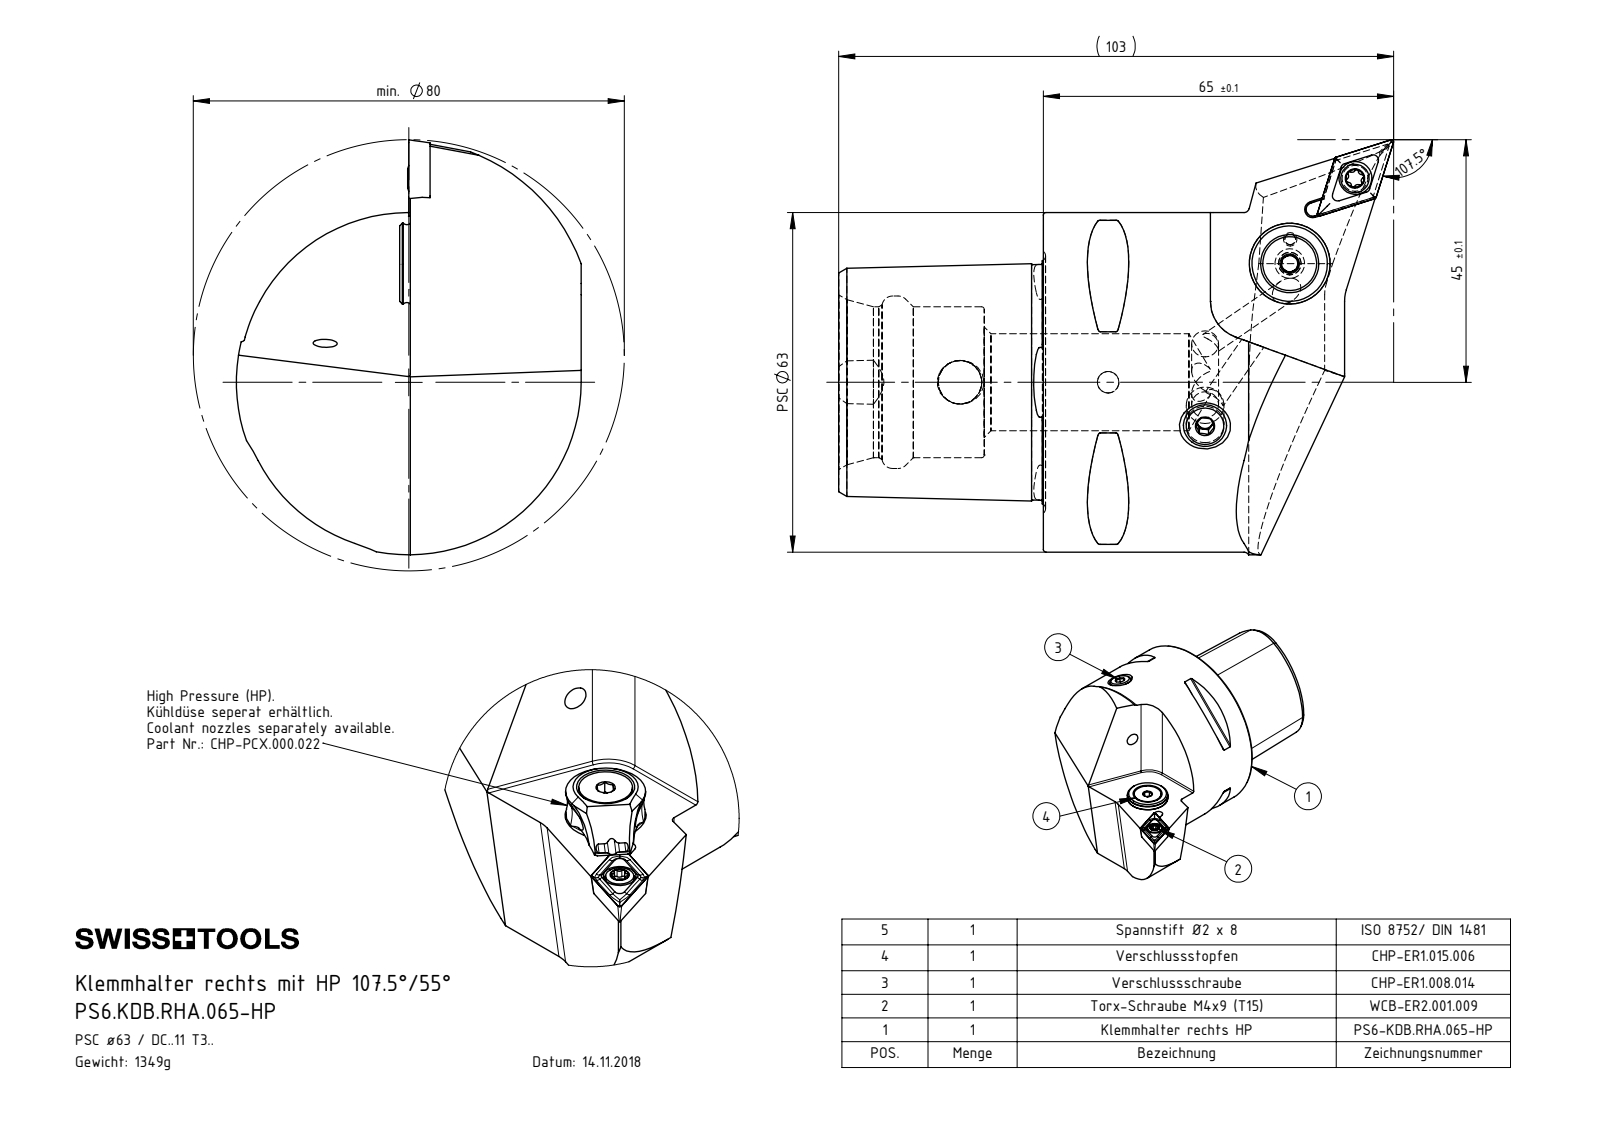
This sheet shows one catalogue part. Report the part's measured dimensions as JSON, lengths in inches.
{"part_name": "PS6.KDB.RHA.065-HP; PS6-KDB.RHA.065-HP_B; DIN 7991 - M5x15; CHP-ER1.015.006_A (+6 more)", "step_written_by": "SolidWorks 2017 (AUTOMOTIVE_DESIGN)", "units": "inches", "bodies": {"solids": 8, "faces": 378, "planar": 91, "cylindrical": 99, "other": 188}, "overall_size": [4.056, 3.031, 2.52], "volume_in3": 10.49, "surface_area_in2": 48.69, "round_holes": [[0.165, 2], [0.197, 2], [0.047, 1], [0.079, 1], [0.098, 1], [0.118, 1], [0.13, 1], [0.157, 1], [0.173, 1], [0.205, 1], [0.24, 1], [0.276, 1]], "round_bosses_or_shafts": [[2.48, 1], [0.591, 1], [0.528, 1], [0.394, 1], [0.315, 1], [0.217, 1], [0.207, 1], [0.197, 1]], "partial_cylinders_radius": [[0.02, 10], [0.013, 6], [0.023, 6], [0.276, 2], [0.049, 1], [0.236, 1], [1.26, 1], [1.378, 1]], "face_to_face_distances": [1.496, 2.717, 1.22, 1.248, 0.98, 1.071, 0.177, 1.063, 0.433, 1.654], "hole_center_spacings": [0.177, 0.65, 0.656, 0.784, 0.789, 1.083, 1.585, 1.691]}
